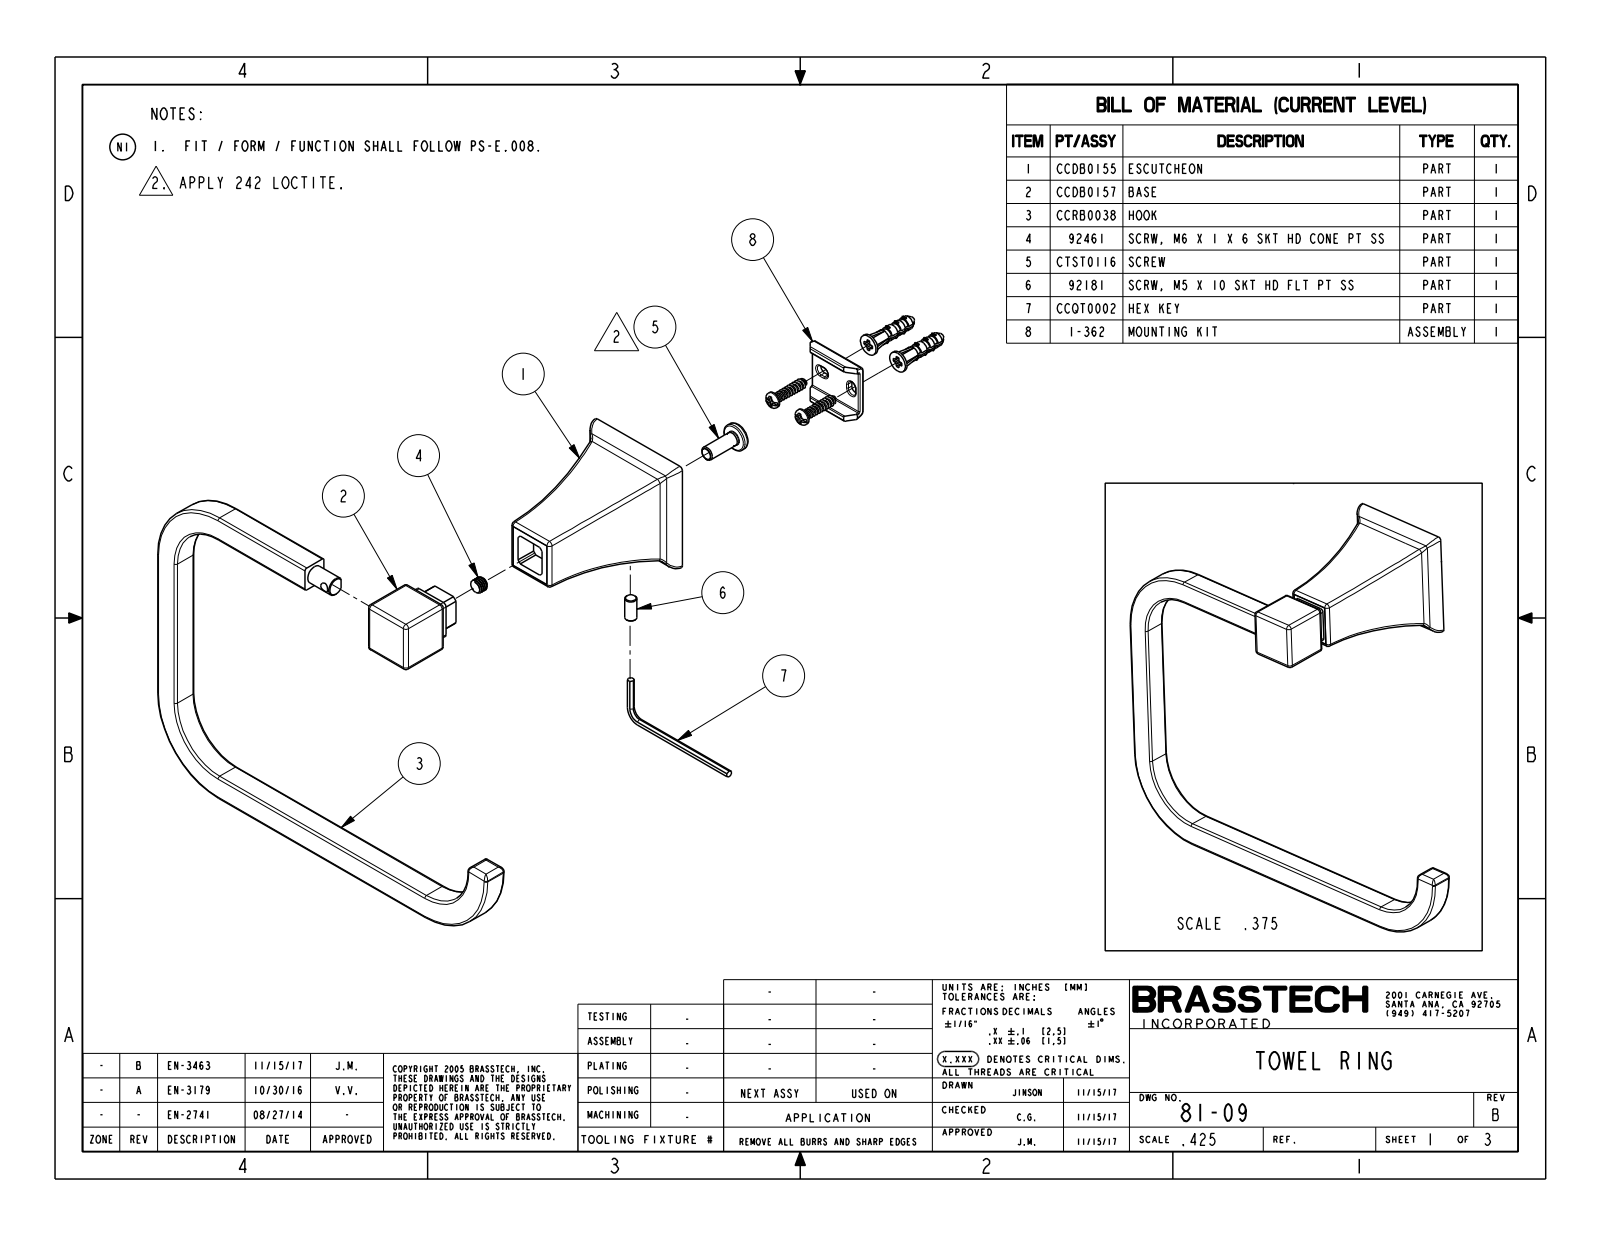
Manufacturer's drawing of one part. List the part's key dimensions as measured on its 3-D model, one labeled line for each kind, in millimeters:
Part name (STEP PRODUCT): CCDB0155; CCDB0157; CCRB0038; CTST0142 (+4 more)
STEP written by: PRO/ENGINEER BY PARAMETRIC TECHNOLOGY CORPORATION, 2013150 (CONFIG_CONTROL_DESIGN)
Units: millimetres
Bodies: 7 solids, 347 faces (121 planar, 143 cylindrical, 83 other)
Overall size (bounding box): 191 × 160.9 × 89
Volume: 78 150 mm³ · Surface area: 42 430 mm²
Round holes (diameter × count): ⌀4 ×1, ⌀4.2 ×1, ⌀5 ×1, ⌀6 ×1, ⌀6.5 ×1, ⌀8.1 ×1, ⌀10 ×1
Round bosses / shafts (diameter × count): ⌀12 ×1, ⌀6 ×1, ⌀5 ×1
Partial cylindrical surfaces — rounded edges, fillets, slot ends (radius × count): R0.5 ×22, R1.5 ×20, R1 ×16, R2 ×6, R2.3 ×4, R4 ×4, R5.3 ×4, R5.5 ×4
Main face-to-face distances: 11, 16.7, 5.7, 2.5, 22.5, 130, 5.5, 9.2, 20.2, 1.5
Hole centre spacings: 1.8
